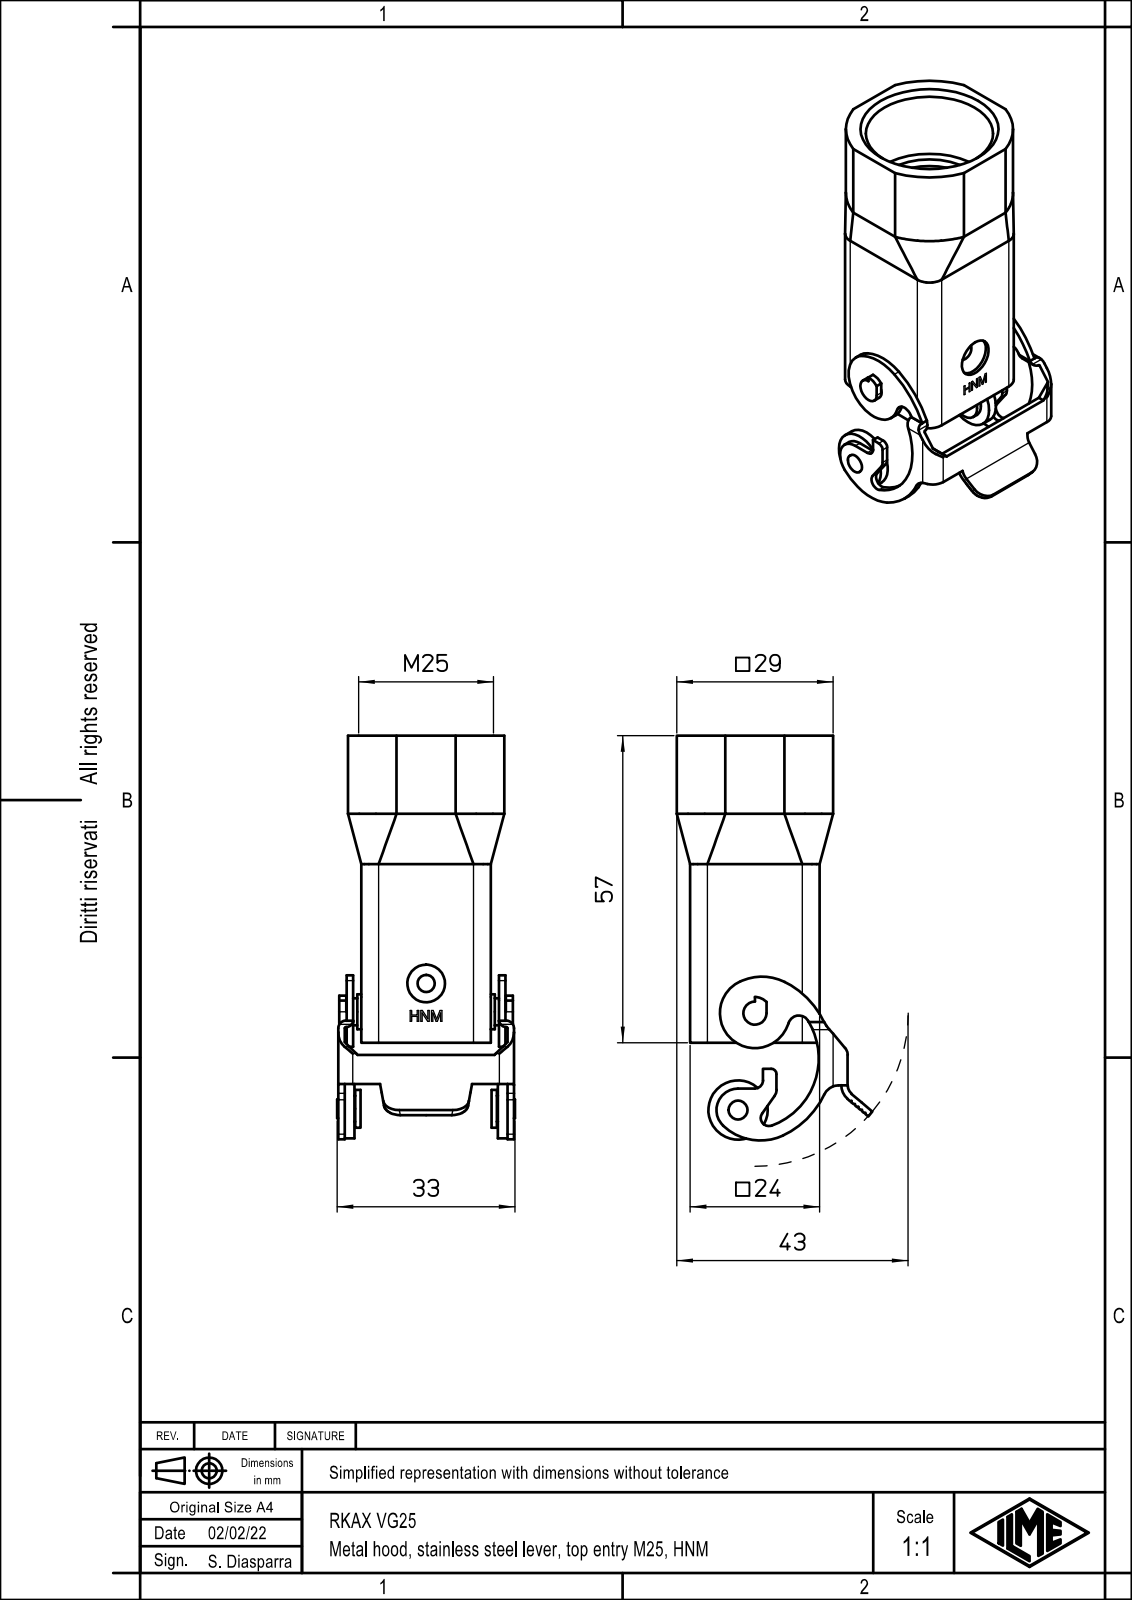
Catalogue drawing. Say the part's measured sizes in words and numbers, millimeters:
The part is named "RKAX_VG25". Its 3-D file was written by "Creo Elements/Direct Modeling 20.1B 02-Apr-2019 (C) Parametric Technology GmbH (AUTOMOTIVE_DESIGN)". It is 1 solid with 376 faces: 250 planar, 117 cylindrical and 9 other. Overall it measures 75.16 by 36.3 by 33 millimeters. Its volume is 11 692 cubic millimeters and its surface area 13 374 square millimeters. Round holes: 1 of diameter 3.2, 1 of diameter 7, 1 of diameter 20, 1 of diameter 23.6. Round bosses or shafts: 1 of diameter 11, 1 of diameter 7, 1 of diameter 6, 1 of diameter 5, 1 of diameter 4.8, 1 of diameter 4.3, 1 of diameter 3.5. Partial cylindrical surfaces (rounded edges, fillets, slot ends): 15 of radius 0.25, 8 of radius 2, 5 of radius 3.2, 4 of radius 1.4, 4 of radius 3, 3 of radius 0.12, 2 of radius 0.2, 2 of radius 1.5. The main face-to-face distances are 1.2, 22.8, 21.6, 24, 25.3, 2.5, 3.7, 26.5, 2.71, 25.51.
